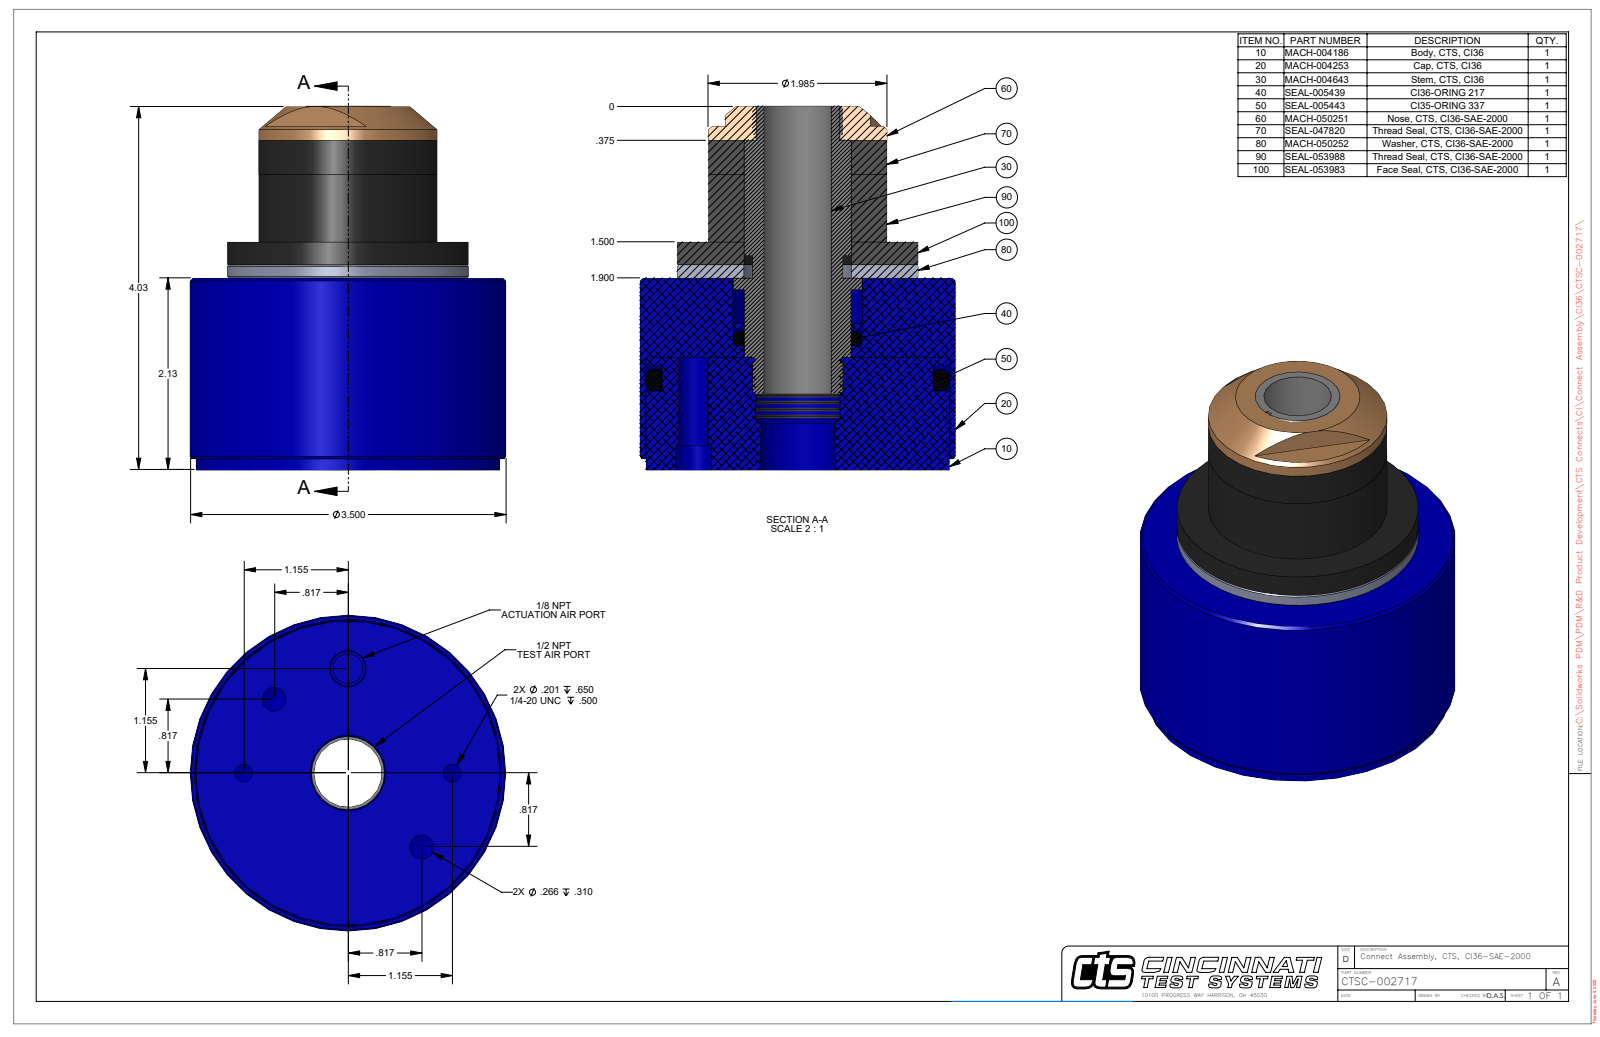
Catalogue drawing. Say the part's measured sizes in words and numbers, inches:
The part is named "CTSC-002717". Its 3-D file was written by "SolidWorks 2023 (AUTOMOTIVE_DESIGN)". It is 1 solid with 87 faces: 24 planar, 35 cylindrical and 28 other. Overall it measures 4.032 by 3.5 by 3.5 inches. Its volume is 24.86 cubic inches and its surface area 81.32 square inches. Round holes: 2 of diameter 0.201, 2 of diameter 0.266, 1 of diameter 0.332, 1 of diameter 0.75, 1 of diameter 0.937, 1 of diameter 1.438, 1 of diameter 3.373. Round bosses or shafts: 1 of diameter 3.5, 1 of diameter 3.365, 1 of diameter 2.675, 1 of diameter 2.67, 1 of diameter 1.985, 1 of diameter 1.98, 1 of diameter 1.427. Partial cylindrical surfaces (rounded edges, fillets, slot ends): 1 of radius 0.461, 1 of radius 0.69. The main face-to-face distances are 2.125, 2.525, 0.4, 4.025, 1.9, 1.5, 3.806, 1.681, 1.281, 0.219. The hole center spacings are 0.884, 1.155, 2.134, 1.155, 1.633, 2.309, 2.31.
